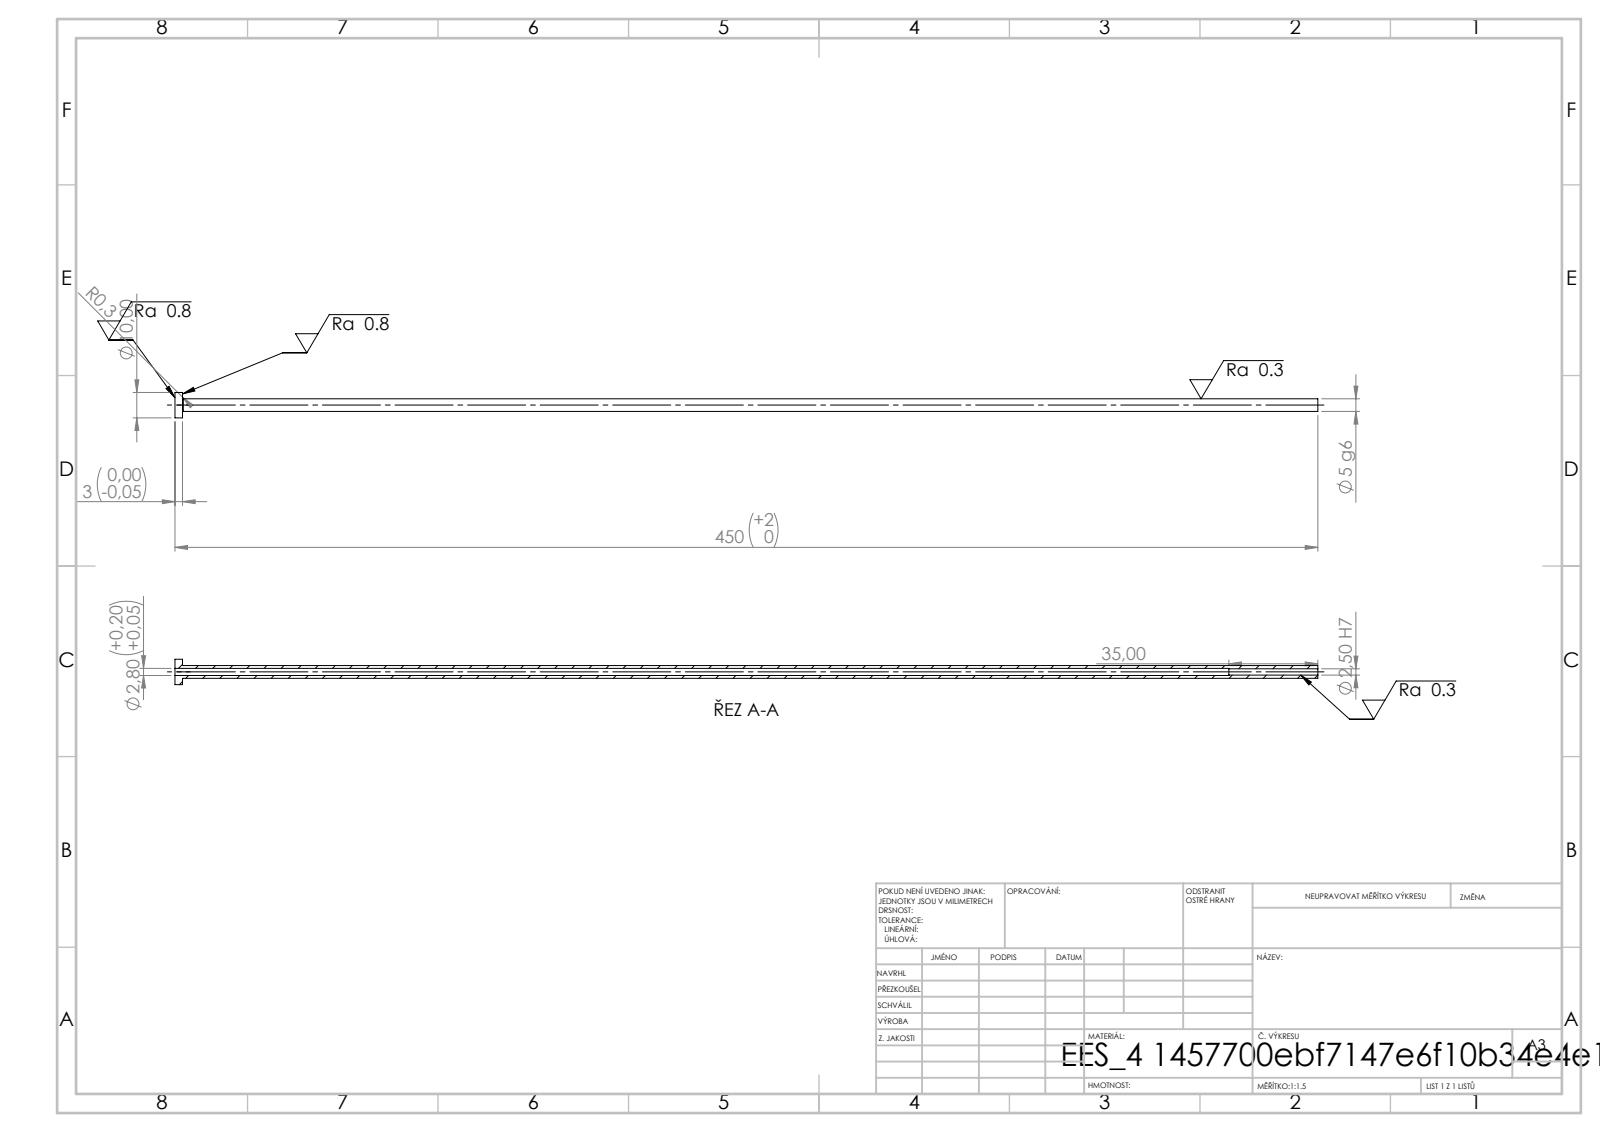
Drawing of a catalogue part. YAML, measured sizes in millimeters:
step_written_by: "SolidWorks 2019 (CONFIG_CONTROL_DESIGN)"
units: millimeters
bodies: {solids: 1, faces: 14, planar: 4, cylindrical: 8, other: 2}
overall_size: [450, 10, 10]
volume: 6286
surface_area: 11186
round_holes:
  - {diameter: 2.5, count: 1}
  - {diameter: 2.8, count: 1}
round_bosses_or_shafts:
  - {diameter: 10, count: 1}
  - {diameter: 5, count: 1}
face_to_face_distances: [3, 450, 447, 415, 412, 35]
